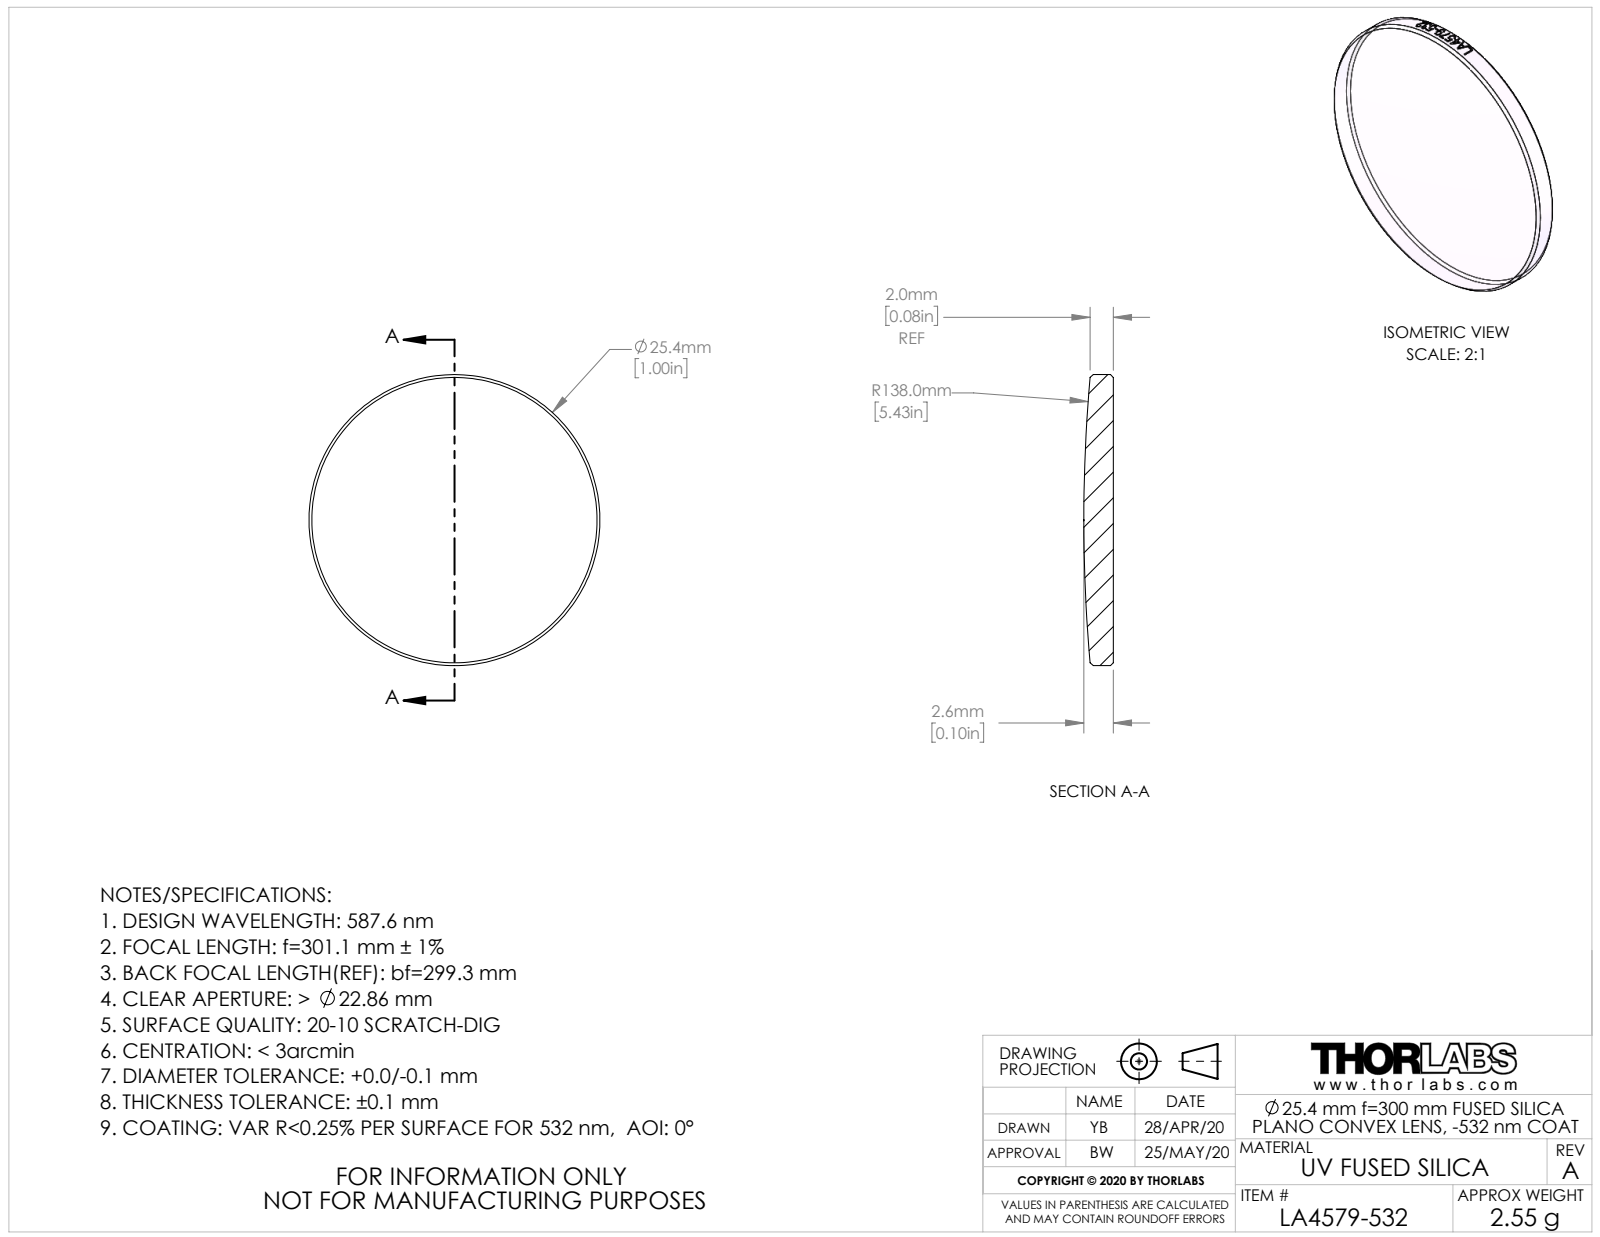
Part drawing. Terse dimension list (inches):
name: CTN015727-E0W
written by: SolidWorks 2018 (AUTOMOTIVE_DESIGN)
unit: in
bodies: 1 solid, 25 faces (1 planar, 18 cylindrical, 6 other)
size: 1 × 1 × 0.102
volume: 0.071 in³; area: 1.786 in²
bosses: 1× ⌀1
